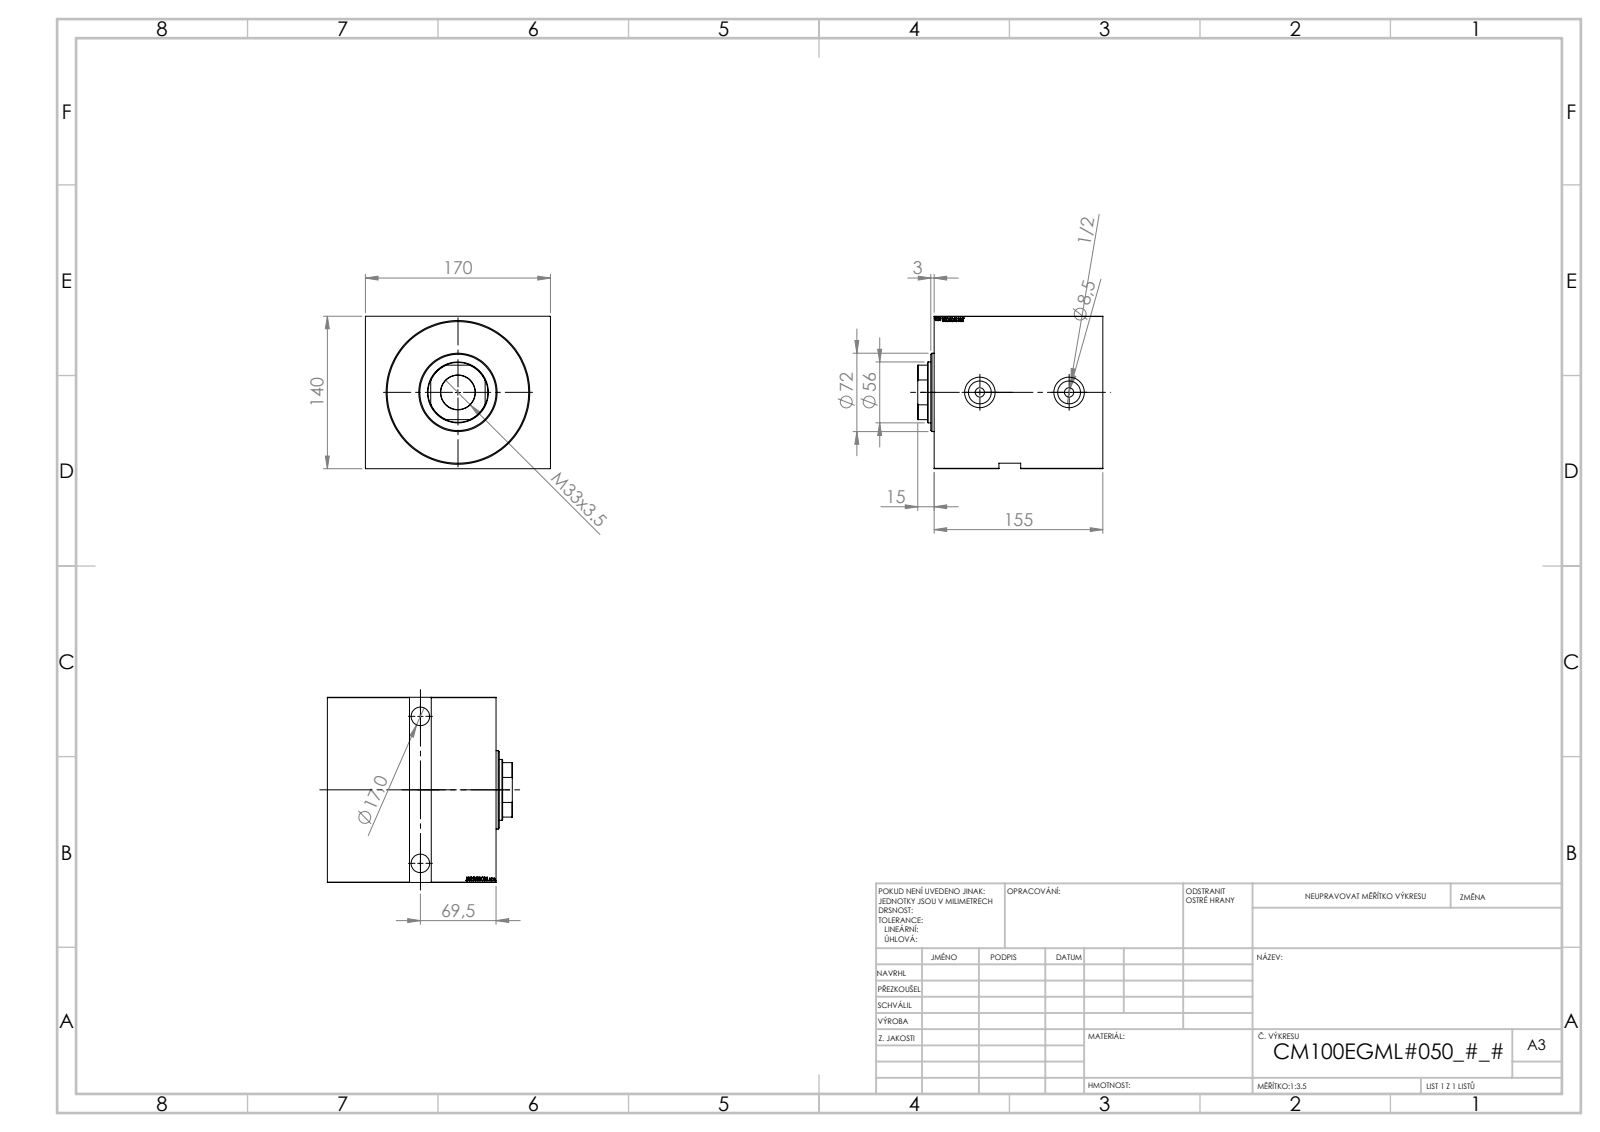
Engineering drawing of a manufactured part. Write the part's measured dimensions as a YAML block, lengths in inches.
part_name: "V450CM_E_VCP; V450CM_VC_B; V450CM_E_Body"
step_written_by: "SolidWorks 2019 (CONFIG_CONTROL_DESIGN)"
units: inches
bodies: {solids: 3, faces: 851, planar: 411, cylindrical: 46, other: 394}
overall_size: [6.693, 6.693, 5.512]
volume: 189.1
surface_area: 437.3
round_holes:
  - {diameter: 0.335, count: 2}
  - {diameter: 0.669, count: 2}
  - {diameter: 0.825, count: 2}
  - {diameter: 0.984, count: 2}
  - {diameter: 1.102, count: 2}
  - {diameter: 1.24, count: 1}
  - {diameter: 1.772, count: 1}
  - {diameter: 1.909, count: 1}
  - {diameter: 3.937, count: 1}
  - {diameter: 4.016, count: 1}
  - {diameter: 5.118, count: 1}
round_bosses_or_shafts:
  - {diameter: 2.835, count: 1}
partial_cylinders:
  - {radius: 0.866, count: 1}
face_to_face_distances: [5.512, 6.693, 6.102, 1.024, 5.079, 0.197, 5.906, 4.882, 5.449, 4.425]
hole_center_spacings: [3.228, 5.315]
